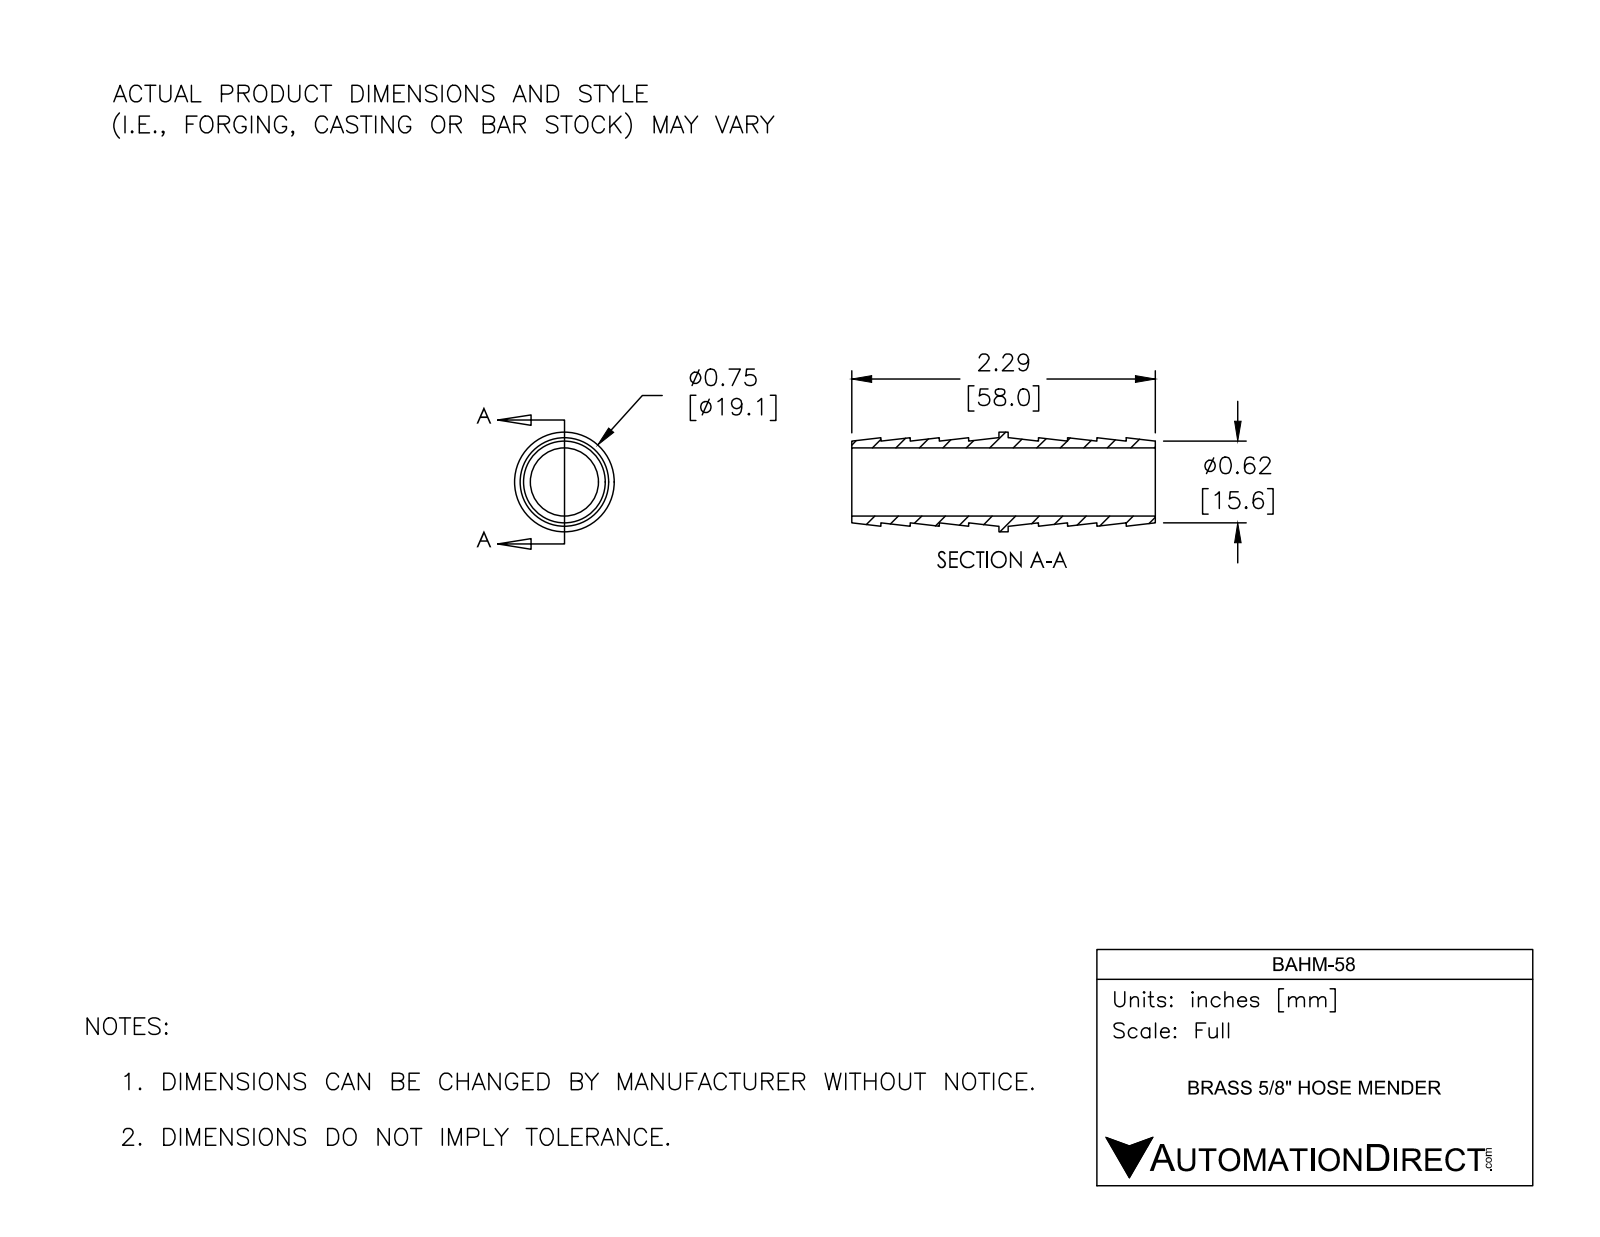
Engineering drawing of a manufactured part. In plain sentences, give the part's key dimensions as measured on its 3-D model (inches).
The part is named "BAHM-58". Its 3-D file was written by "SolidWorks 2017 (AUTOMOTIVE_DESIGN)". It is 1 solid with 40 faces: 12 planar, 8 cylindrical and 20 other. Overall it measures 2.285 by 0.751 by 0.751 inches. Its volume is 0.276 cubic inches and its surface area 9.121 square inches. Round holes: 1 of diameter 0.512. Round bosses or shafts: 1 of diameter 0.751, 1 of diameter 0.667. The main face-to-face distances are 0.22, 0.66, 0.44, 1.405, 1.185, 1.107, 1.178, 1.845, 0.44, 0.88.
